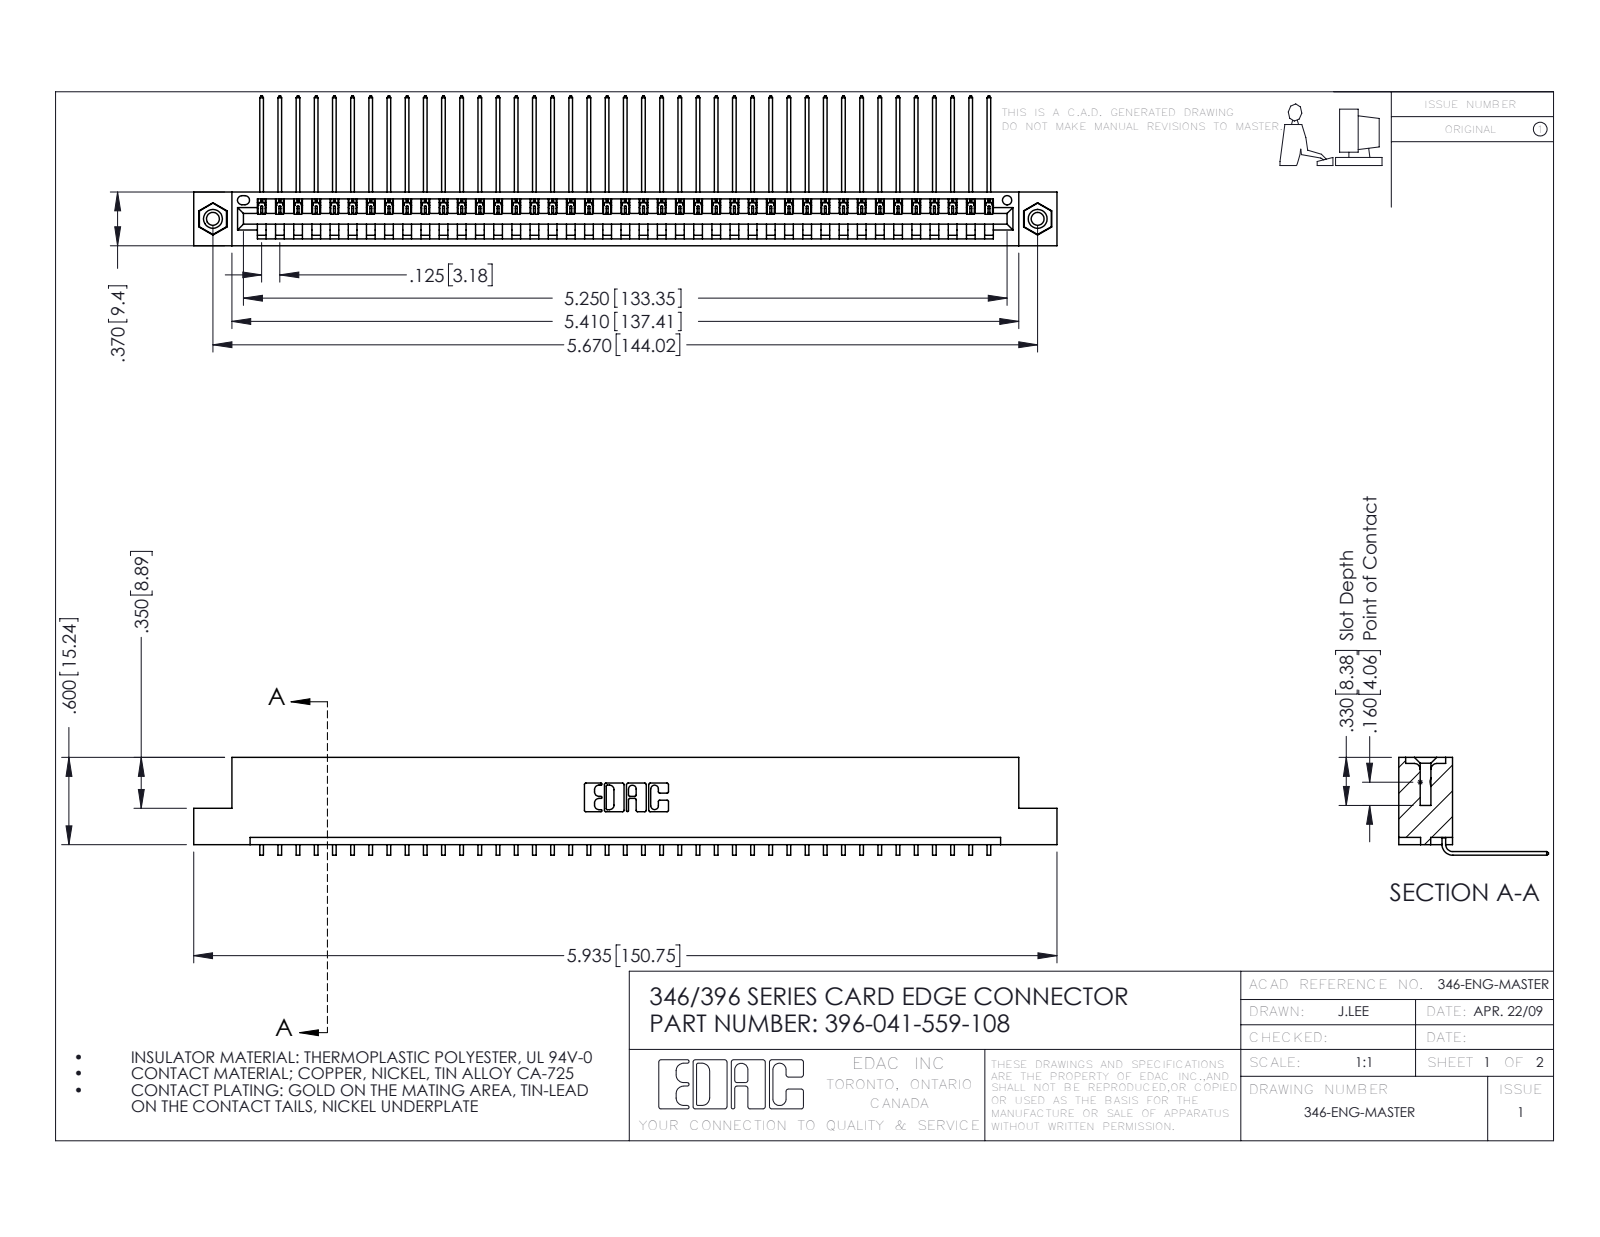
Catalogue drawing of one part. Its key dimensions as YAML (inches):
part_name: "345-250-001_345-250-003-102; 346 Part_Flush Mounting Lugs - 0.156 Dia-TI; 396-041-559-108; 345-292-001_558 559 Tail - 1"
step_written_by: "SolidWorks 2016 (CONFIG_CONTROL_DESIGN)"
units: inches
bodies: {solids: 44, faces: 2642, planar: 1830, cylindrical: 796, other: 16}
overall_size: [5.935, 1.03, 0.673]
volume: 0.888
surface_area: 29.47
round_holes:
  - {diameter: 0.089, count: 2}
  - {diameter: 0.125, count: 2}
  - {diameter: 0.156, count: 2}
  - {diameter: 0.064, count: 1}
round_bosses_or_shafts:
  - {diameter: 0.155, count: 2}
partial_cylinders:
  - {radius: 0.006, count: 82}
  - {radius: 0.01, count: 22}
  - {radius: 0.007, count: 6}
  - {radius: 0.031, count: 6}
  - {radius: 0.026, count: 3}
  - {radius: 0.031, count: 2}
  - {radius: 0.04, count: 2}
  - {radius: 0.014, count: 1}
face_to_face_distances: [0.048, 0.322, 0.37, 0.025, 0.072, 0.25, 0.298, 0.148, 0.222, 0.1]
hole_center_spacings: [0.246, 5.461, 5.67]
